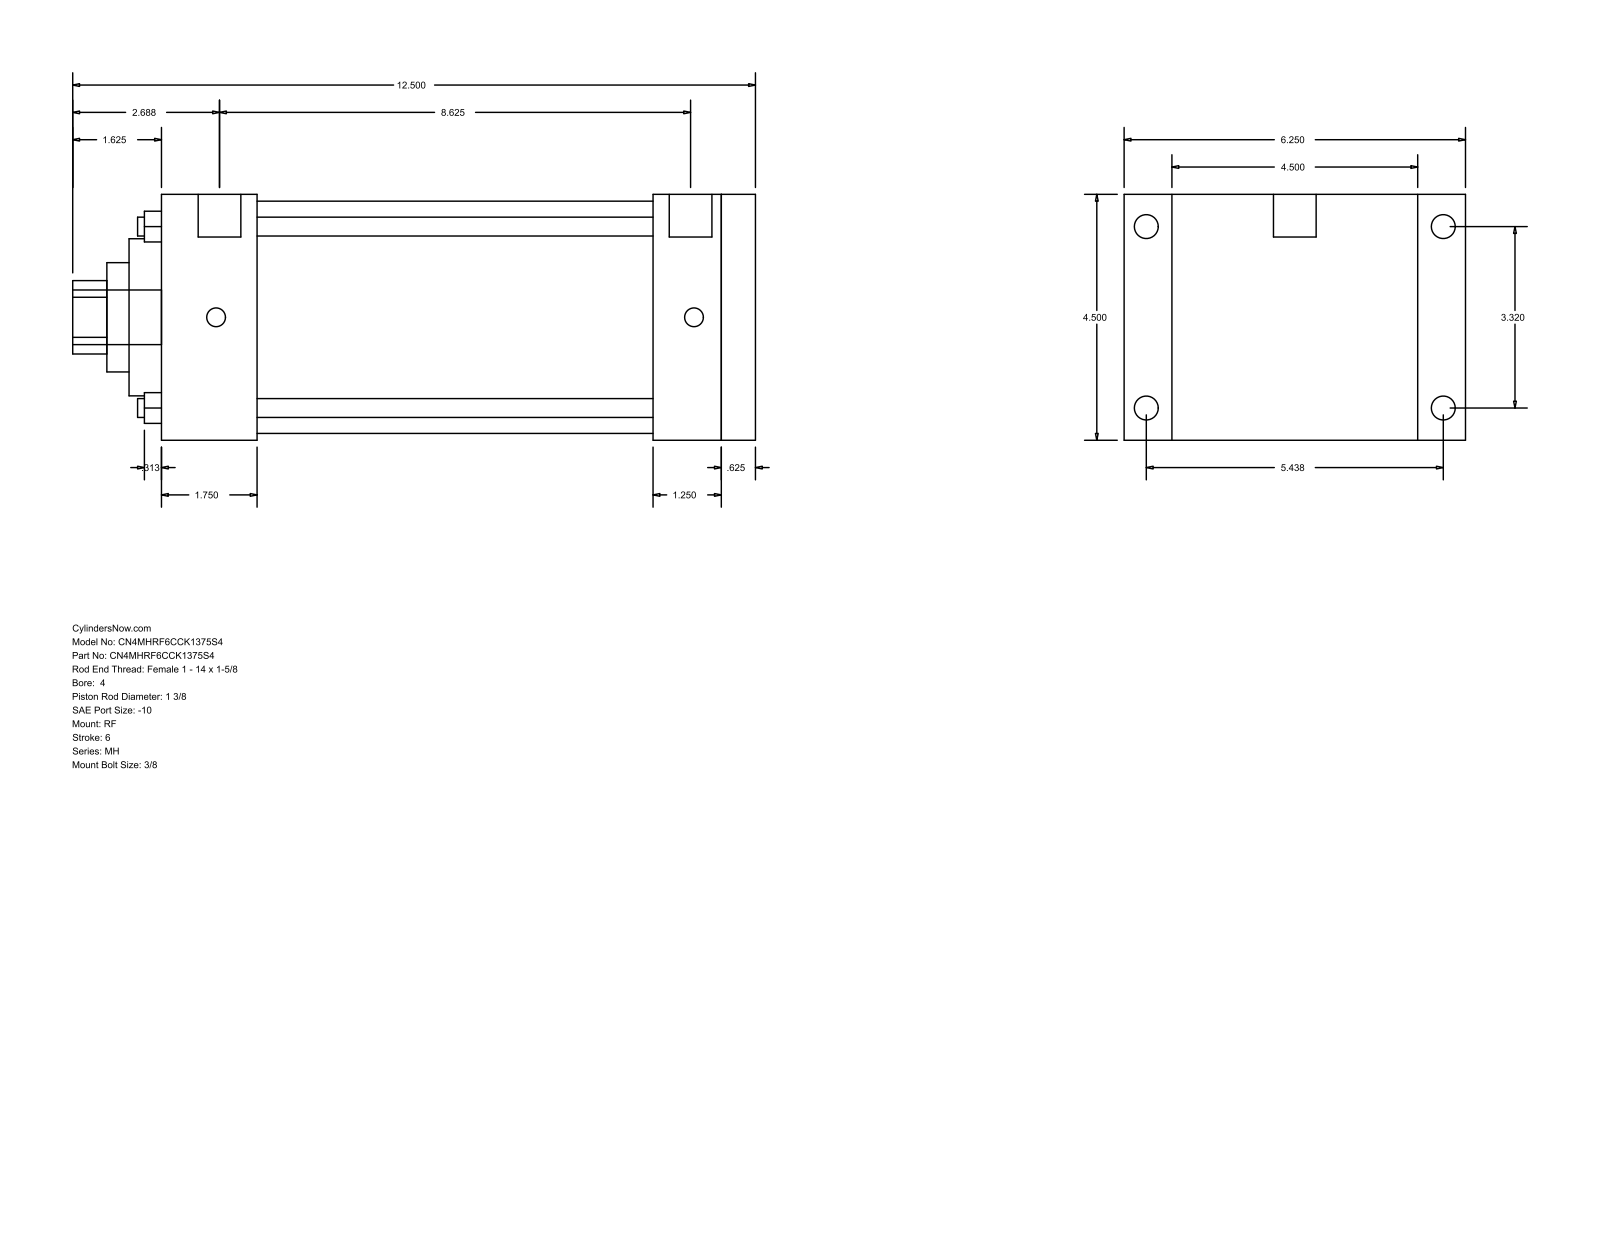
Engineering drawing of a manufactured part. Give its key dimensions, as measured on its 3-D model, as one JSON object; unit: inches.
{"part_name": "MH_RF__0400_1.375", "step_written_by": "GSSL Pune (CONFIG_CONTROL_DESIGN)", "units": "inches", "bodies": {"solids": 0, "faces": 94, "planar": 65, "cylindrical": 29, "other": 0}, "overall_size": [12.5, 6.25, 4.5], "round_holes": [[0.345, 4], [1.375, 1], [2, 1], [2.875, 1], [4.25, 1]], "round_bosses_or_shafts": [[0.438, 4], [0.344, 4], [0.781, 2], [1, 1]], "partial_cylinders_radius": [[0.672, 1]], "face_to_face_distances": [4.5, 10.875, 0.625, 10.25, 1.75, 8.5, 9.125, 9, 7.25, 1.25], "hole_center_spacings": [2.347, 3.32, 4.695]}
